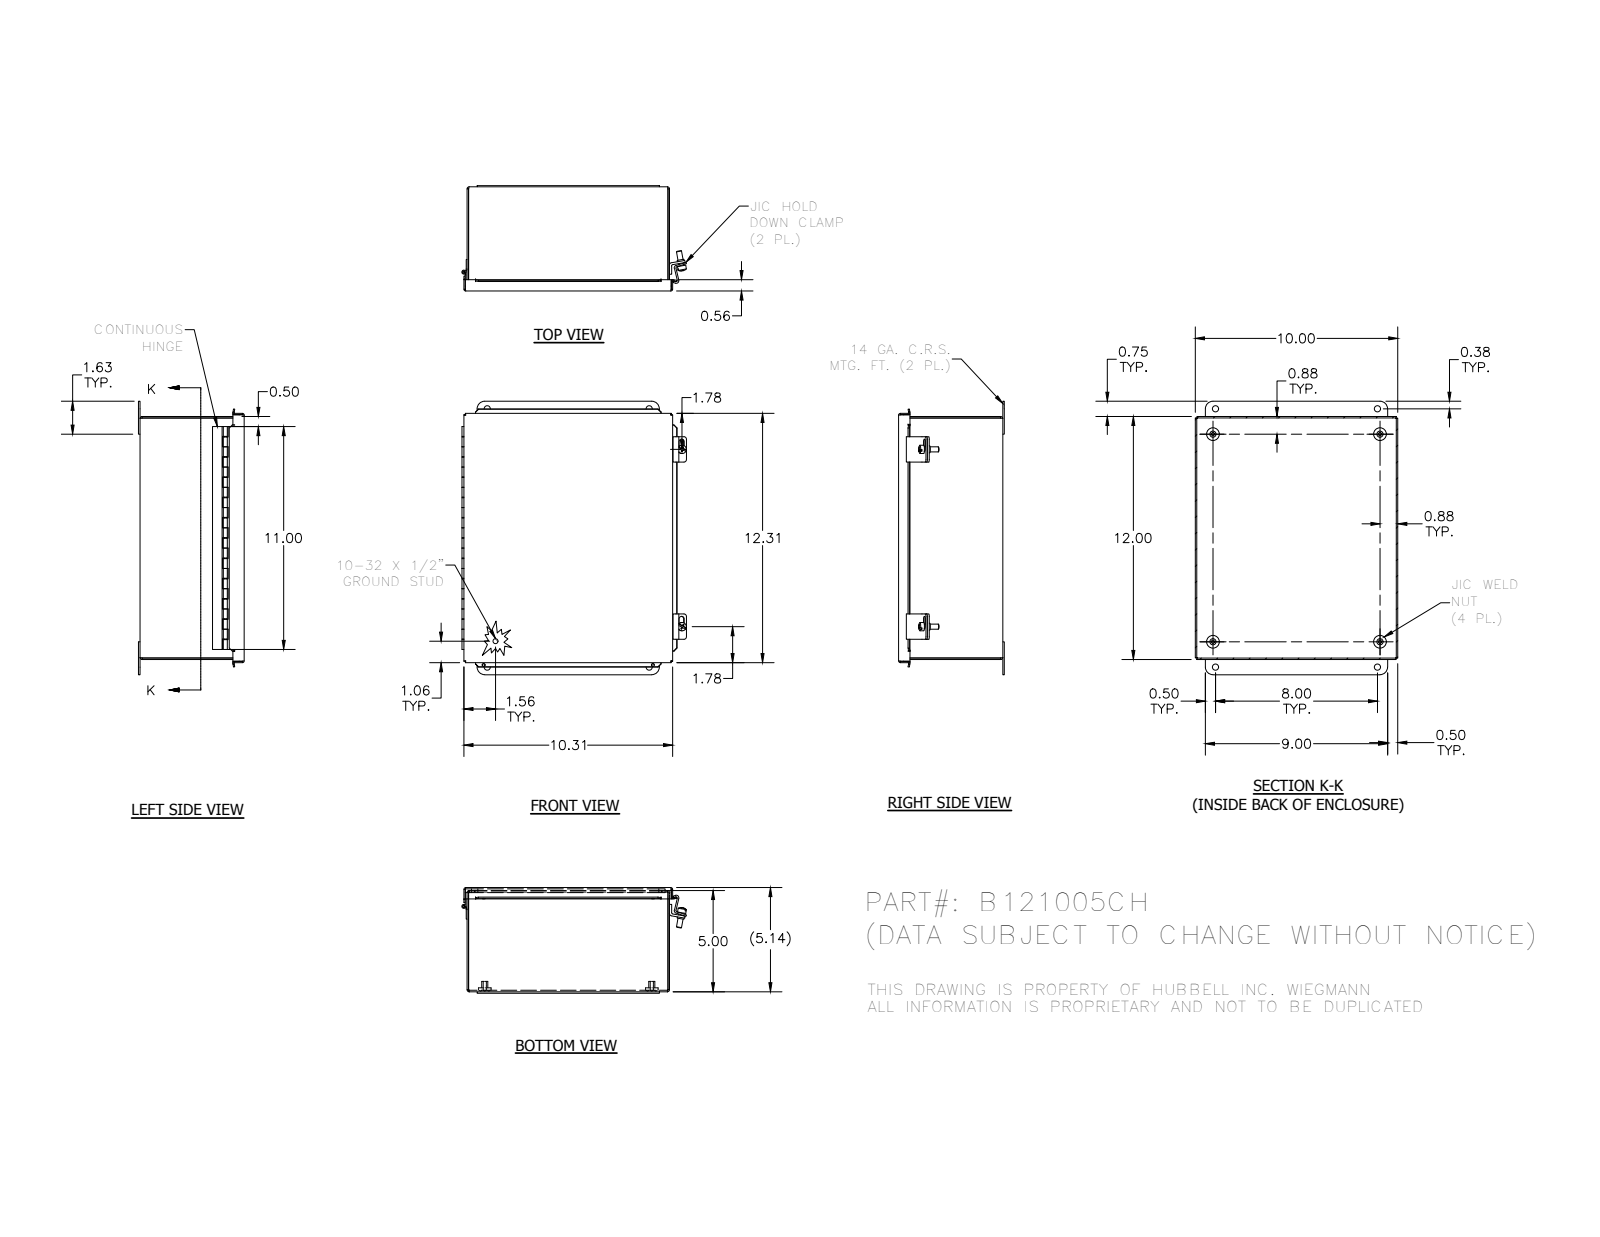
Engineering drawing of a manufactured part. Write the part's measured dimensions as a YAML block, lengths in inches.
part_name: "B121005CH; 3499; 3484; C1001 (+8 more)"
step_written_by: "Autodesk Inventor 2012 (AUTOMOTIVE_DESIGN)"
units: inches
bodies: {solids: 20, faces: 499, planar: 323, cylindrical: 131, other: 45}
overall_size: [13.5, 11.087, 5.219]
volume: 44.04
surface_area: 1207
round_holes:
  - {diameter: 0.156, count: 4}
  - {diameter: 0.31, count: 4}
  - {diameter: 0.14, count: 2}
  - {diameter: 0.196, count: 2}
  - {diameter: 0.116, count: 1}
round_bosses_or_shafts:
  - {diameter: 0.625, count: 4}
  - {diameter: 0.3, count: 4}
  - {diameter: 0.25, count: 3}
  - {diameter: 0.41, count: 2}
  - {diameter: 0.344, count: 2}
  - {diameter: 0.2, count: 1}
  - {diameter: 0.19, count: 1}
  - {diameter: 0.1, count: 1}
partial_cylinders:
  - {radius: 0.031, count: 15}
  - {radius: 0.105, count: 8}
  - {radius: 0.125, count: 8}
  - {radius: 0.093, count: 7}
  - {radius: 0.133, count: 4}
  - {radius: 0.375, count: 4}
  - {radius: 0.063, count: 3}
  - {radius: 0.126, count: 3}
face_to_face_distances: [0.074, 5.083, 5.144, 0.062, 5.009, 5.07, 9.926, 11.926, 10, 9.852]
hole_center_spacings: [1.257, 8.221, 11.501, 14.081, 8, 12.75, 15.052, 1.256]
